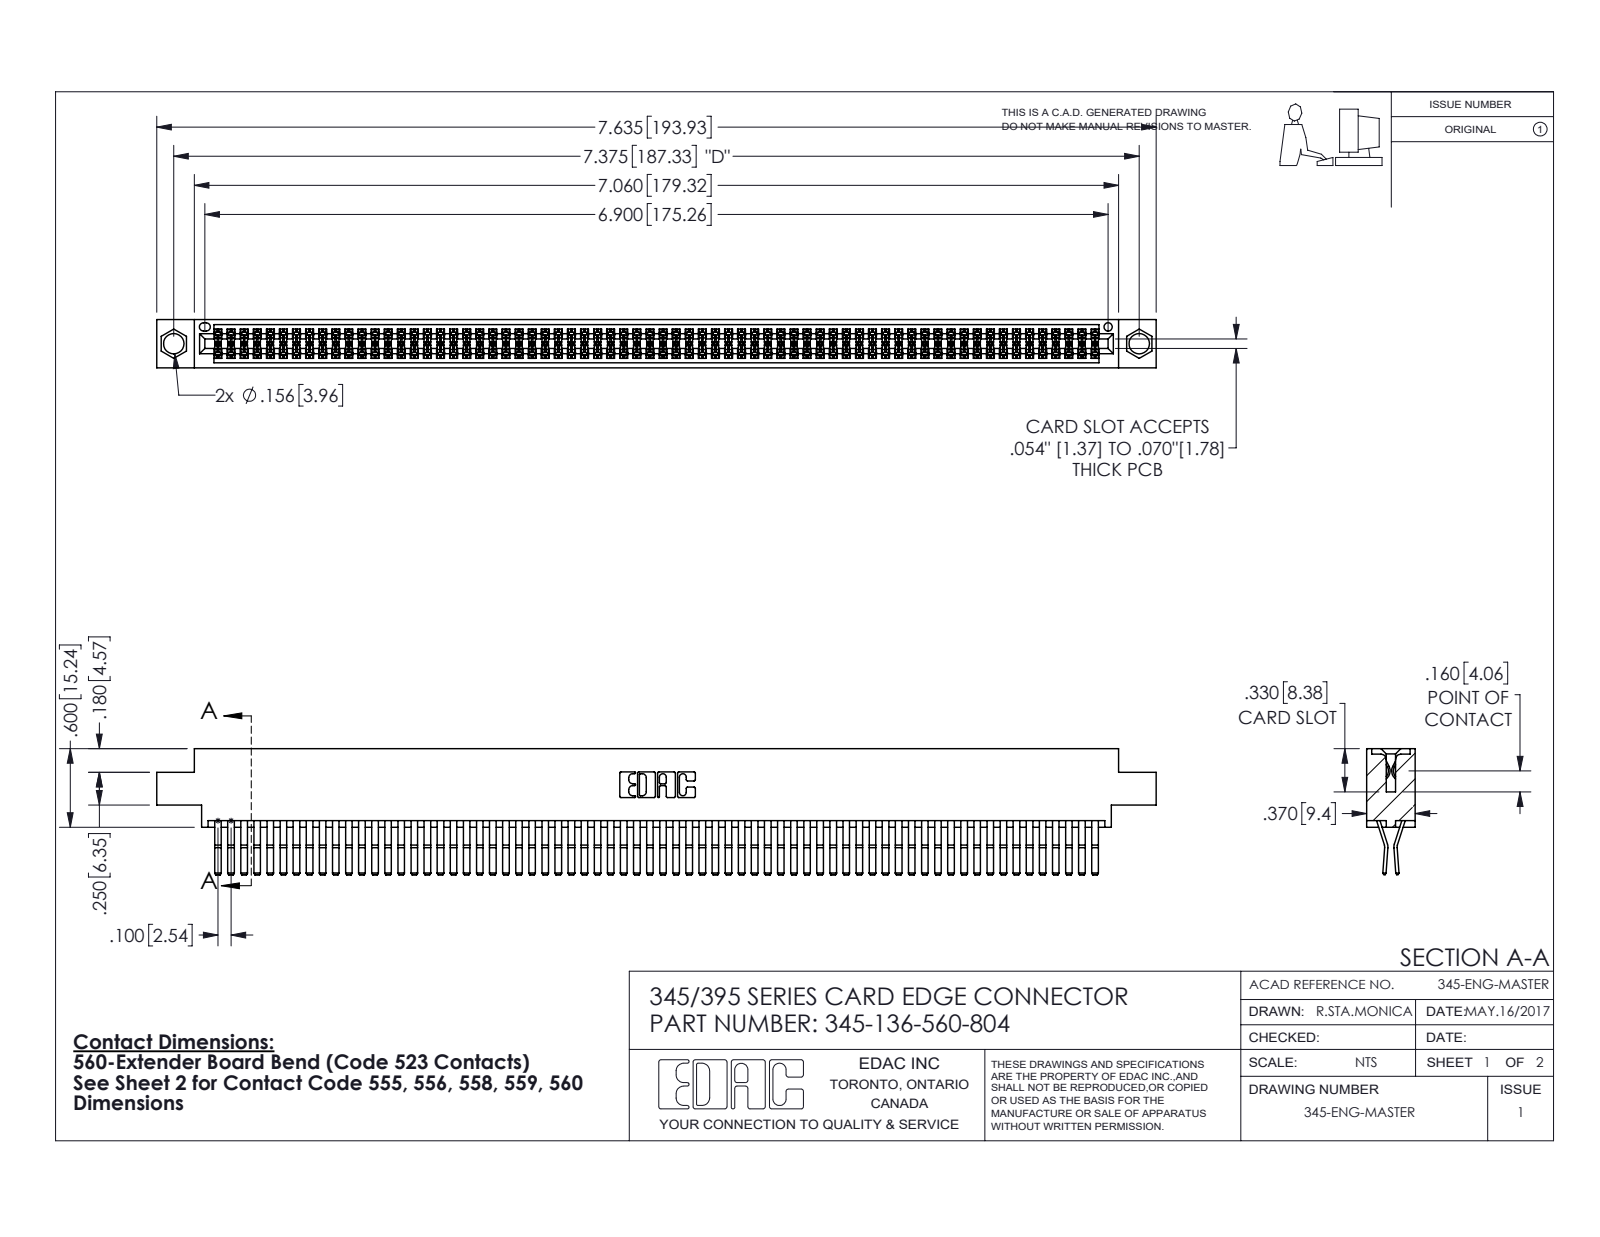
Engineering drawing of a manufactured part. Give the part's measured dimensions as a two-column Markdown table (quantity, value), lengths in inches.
| quantity | value |
| --- | --- |
| part name | 345 Part_0.170 Offset - 0.156 Dia-TI; 345-292-001_560 Tail; 345-136-560-804 |
| STEP written by | SolidWorks 2020 (CONFIG_CONTROL_DESIGN) |
| units | inches |
| bodies | 137 solids, 7216 faces (4586 planar, 2630 cylindrical, 0 other) |
| overall size | 7.635 × 0.962 × 0.37 |
| volume | 1.205 in³ |
| surface area | 49.58 in² |
| round holes (diameter × count) | 0.156 × 2, 0.064 × 1 |
| partial cylindrical surfaces (radius × count) | 0.006 × 204, 0.01 × 22, 0.007 × 6, 0.031 × 6, 0.026 × 3, 0.01 × 2, 0.014 × 2, 0.019 × 2 |
| main face-to-face distances | 0.025, 0.298, 0.072, 0.37, 0.2, 0.098, 0.272, 0.225, 0.175, 0.149 |
| hole center spacings | 0.27, 7.139, 7.375 |
